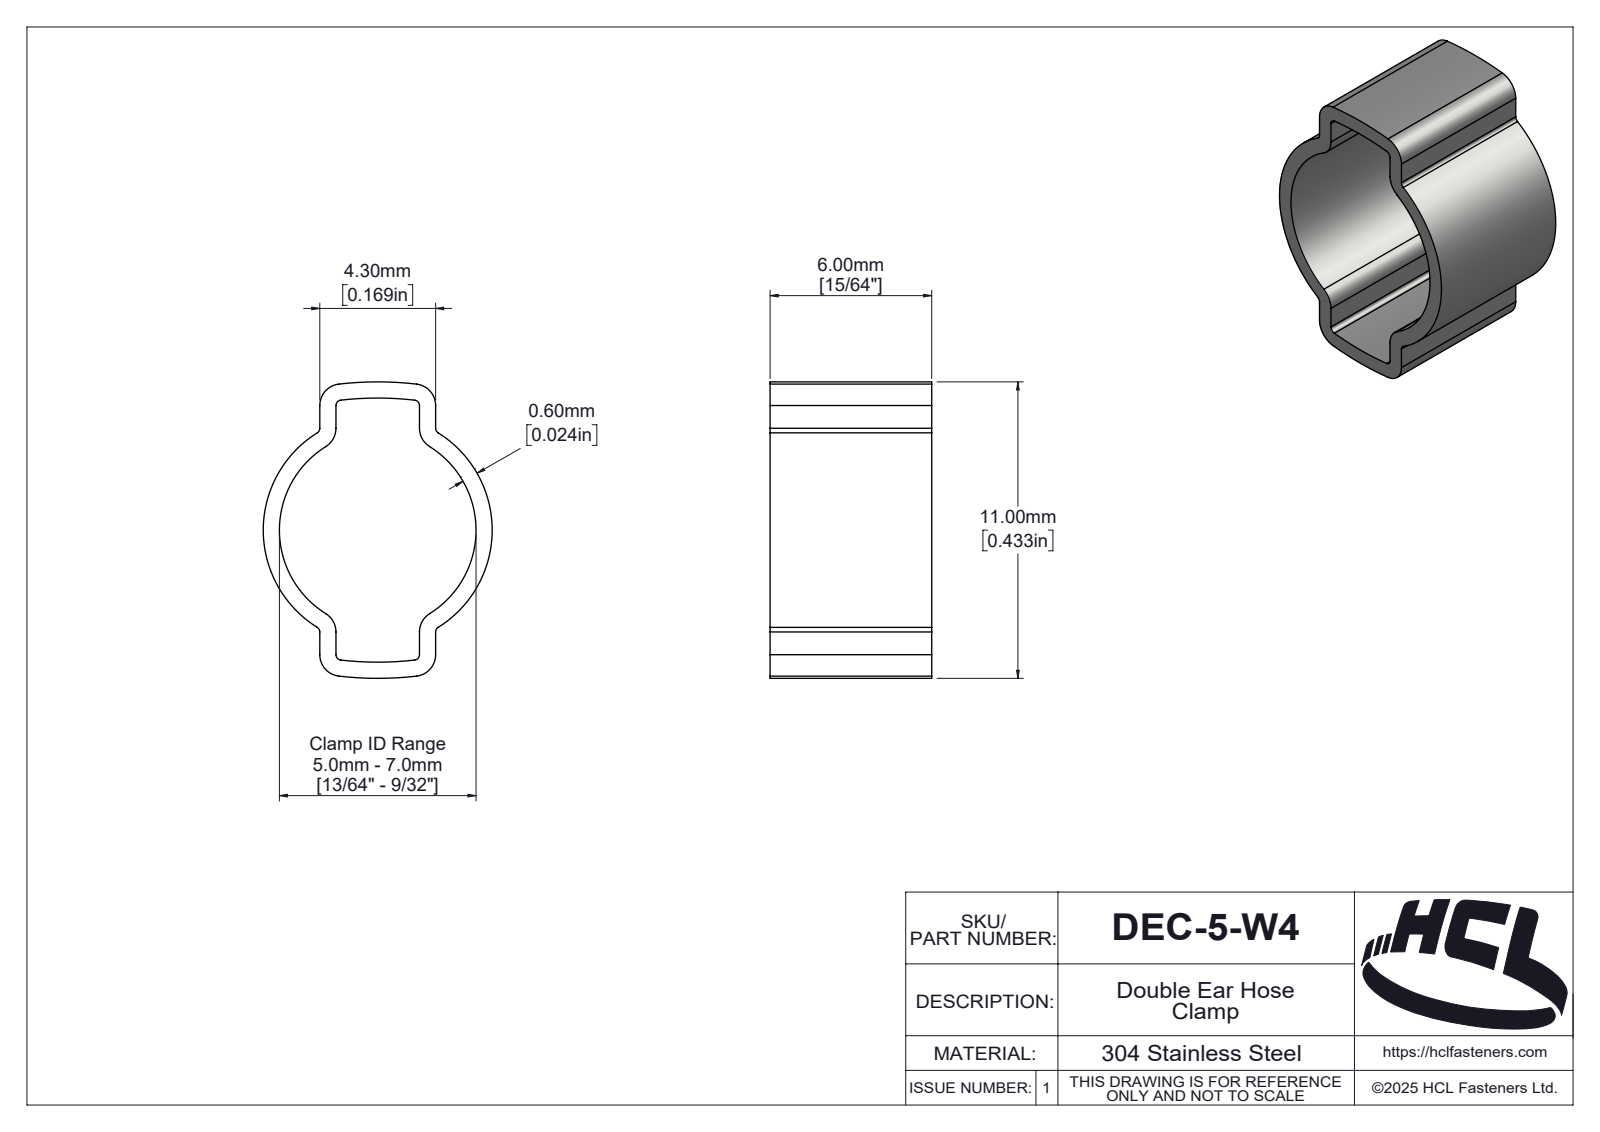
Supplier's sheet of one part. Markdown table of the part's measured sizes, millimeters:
| quantity | value |
| --- | --- |
| part name | DEC-5-W4 |
| STEP written by | SolidWorks 2025 (AUTOMOTIVE_DESIGN) |
| units | millimeters |
| bodies | 1 solid, 137 faces (12 planar, 76 cylindrical, 49 other) |
| overall size | 11 × 8.5 × 6 |
| volume | 108 mm³ |
| surface area | 398 mm² |
| partial cylindrical surfaces (radius × count) | 0.2 × 8, 0.8 × 8, 12.06 × 2, 12.66 × 2, 0.13 × 1, 0.54 × 1, 0.67 × 1, 0.71 × 1 |
| main face-to-face distances | 0.6, 3.7, 6, 4.3, 3.1, 1.97, 1.37, 1.73, 2.33, 2.07 |
